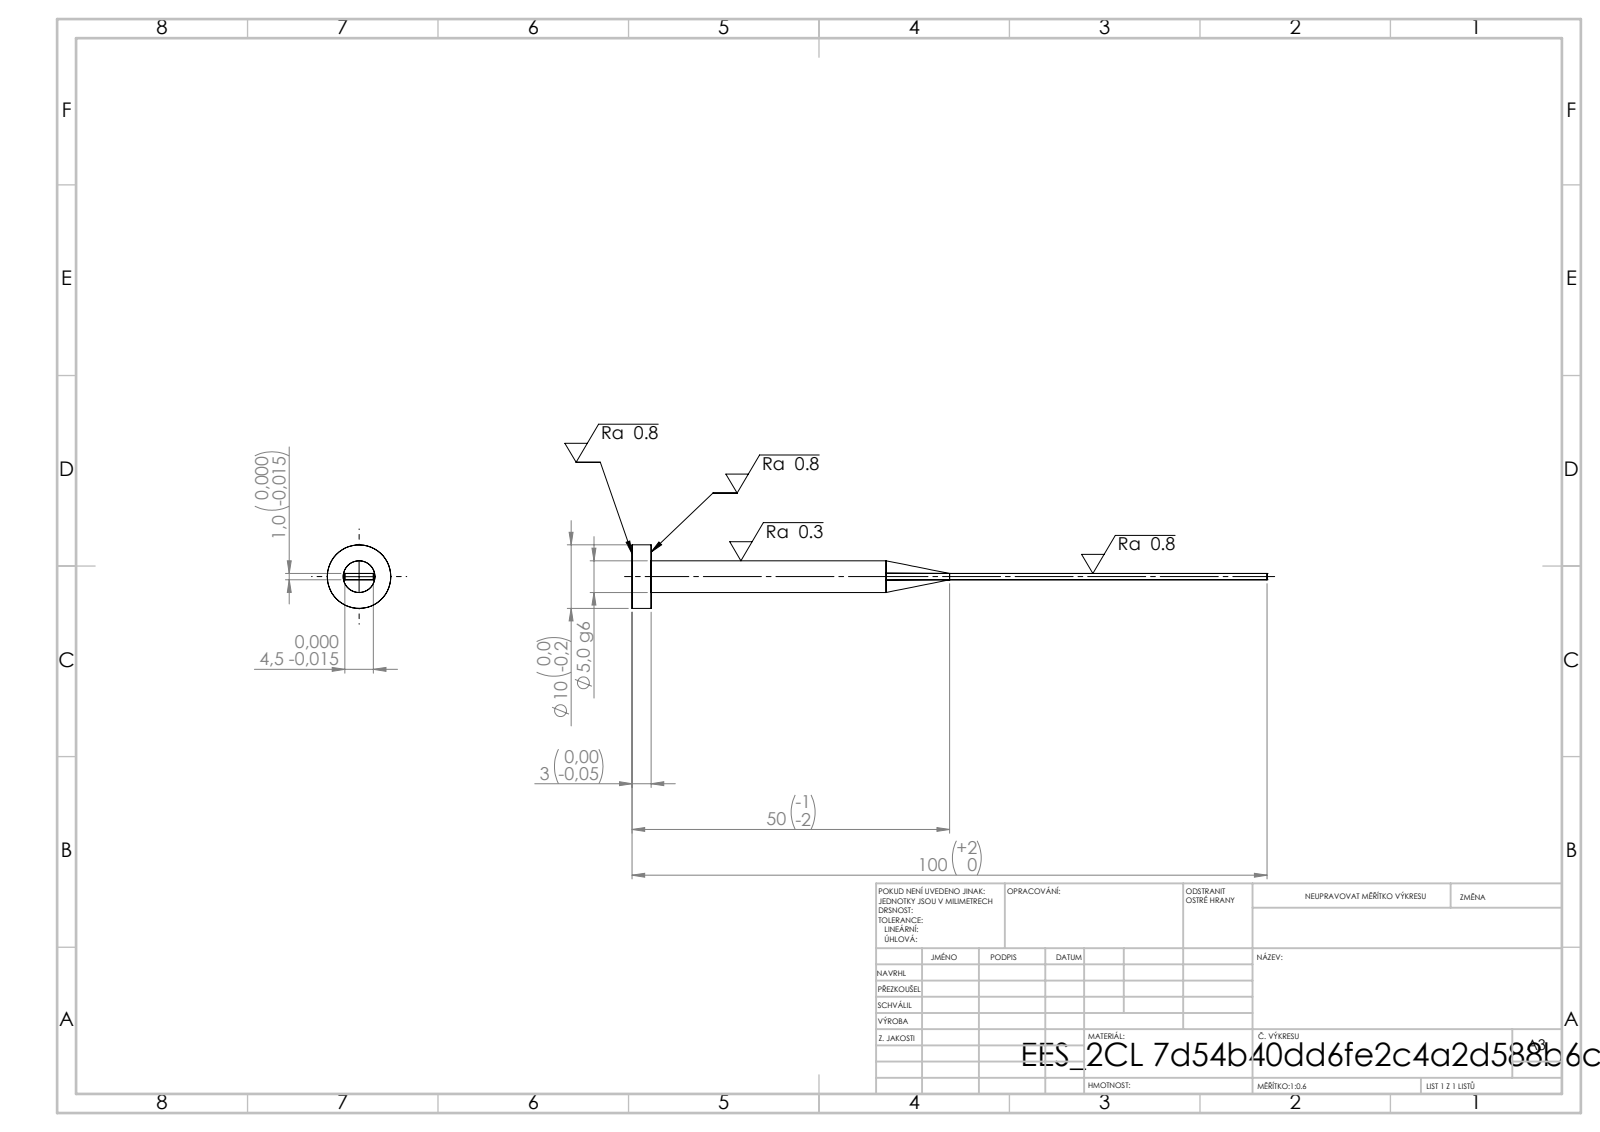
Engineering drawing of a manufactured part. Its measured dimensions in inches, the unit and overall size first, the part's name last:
Units: inches
Overall size (bounding box): 3.937 × 0.394 × 0.394
Round bosses / shafts (diameter × count): ⌀0.394 ×1, ⌀0.197 ×1
Main face-to-face distances: 0.039, 0.118, 0.177, 3.937, 3.819
Volume: 0.079 in³ · Surface area: 2.319 in²
Bodies: 1 solid, 15 faces (7 planar, 4 cylindrical, 4 other)
STEP written by: SolidWorks 2019 (CONFIG_CONTROL_DESIGN)
